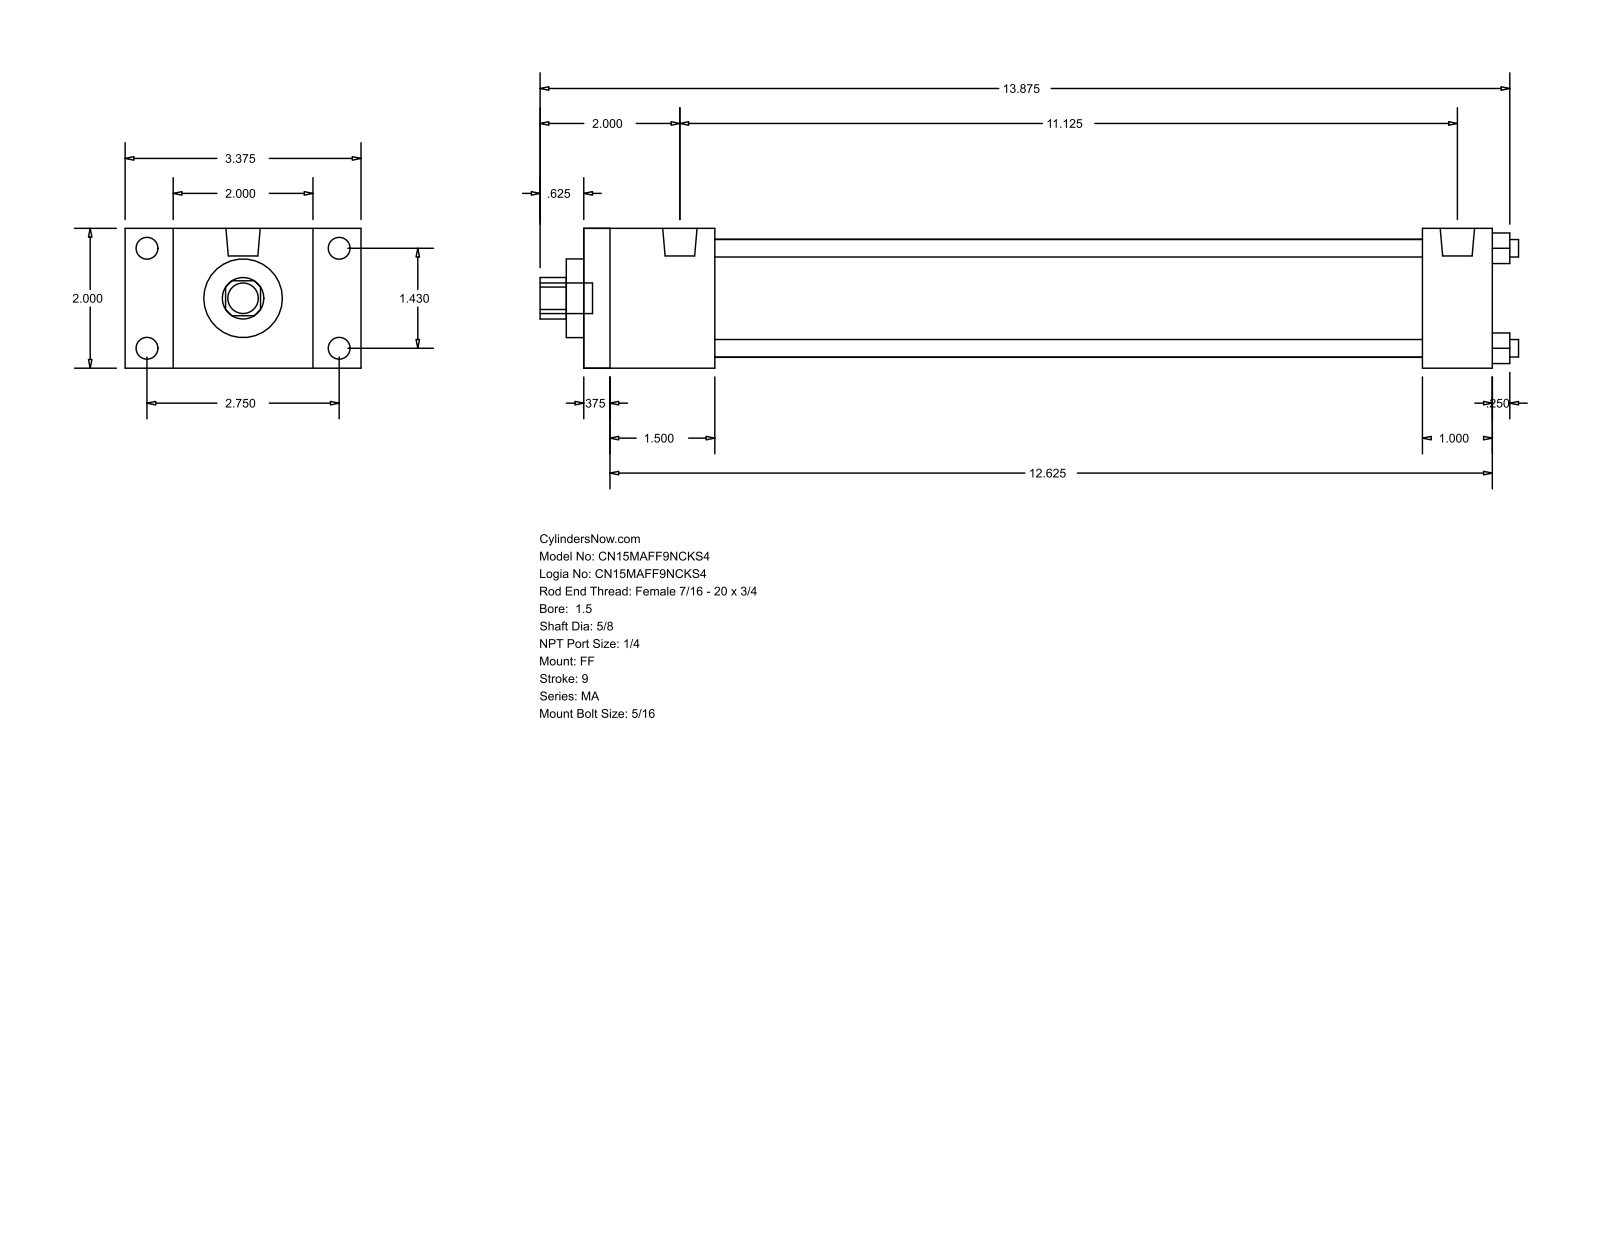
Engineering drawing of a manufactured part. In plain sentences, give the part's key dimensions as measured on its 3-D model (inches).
The part is named "MA_FF__0150_0.625". Its 3-D file was written by "GSSL Pune (CONFIG_CONTROL_DESIGN)". It is 0 solids with 92 faces: 64 planar, 28 cylindrical and 0 other. Overall it measures 14 by 3.375 by 2 inches. Round holes: 4 of diameter 0.25, 1 of diameter 0.625, 1 of diameter 1.125, 1 of diameter 1.69. Round bosses or shafts: 8 of diameter 0.313, 2 of diameter 0.492, 1 of diameter 0.437. Partial cylindrical surfaces (rounded edges, fillets, slot ends): 1 of radius 0.297. The main face-to-face distances are 2, 13, 0.375, 12.625, 1.875, 12, 1.5, 11.625, 10.125, 11.125. The hole center spacings are 1.011, 1.43, 2.022.
